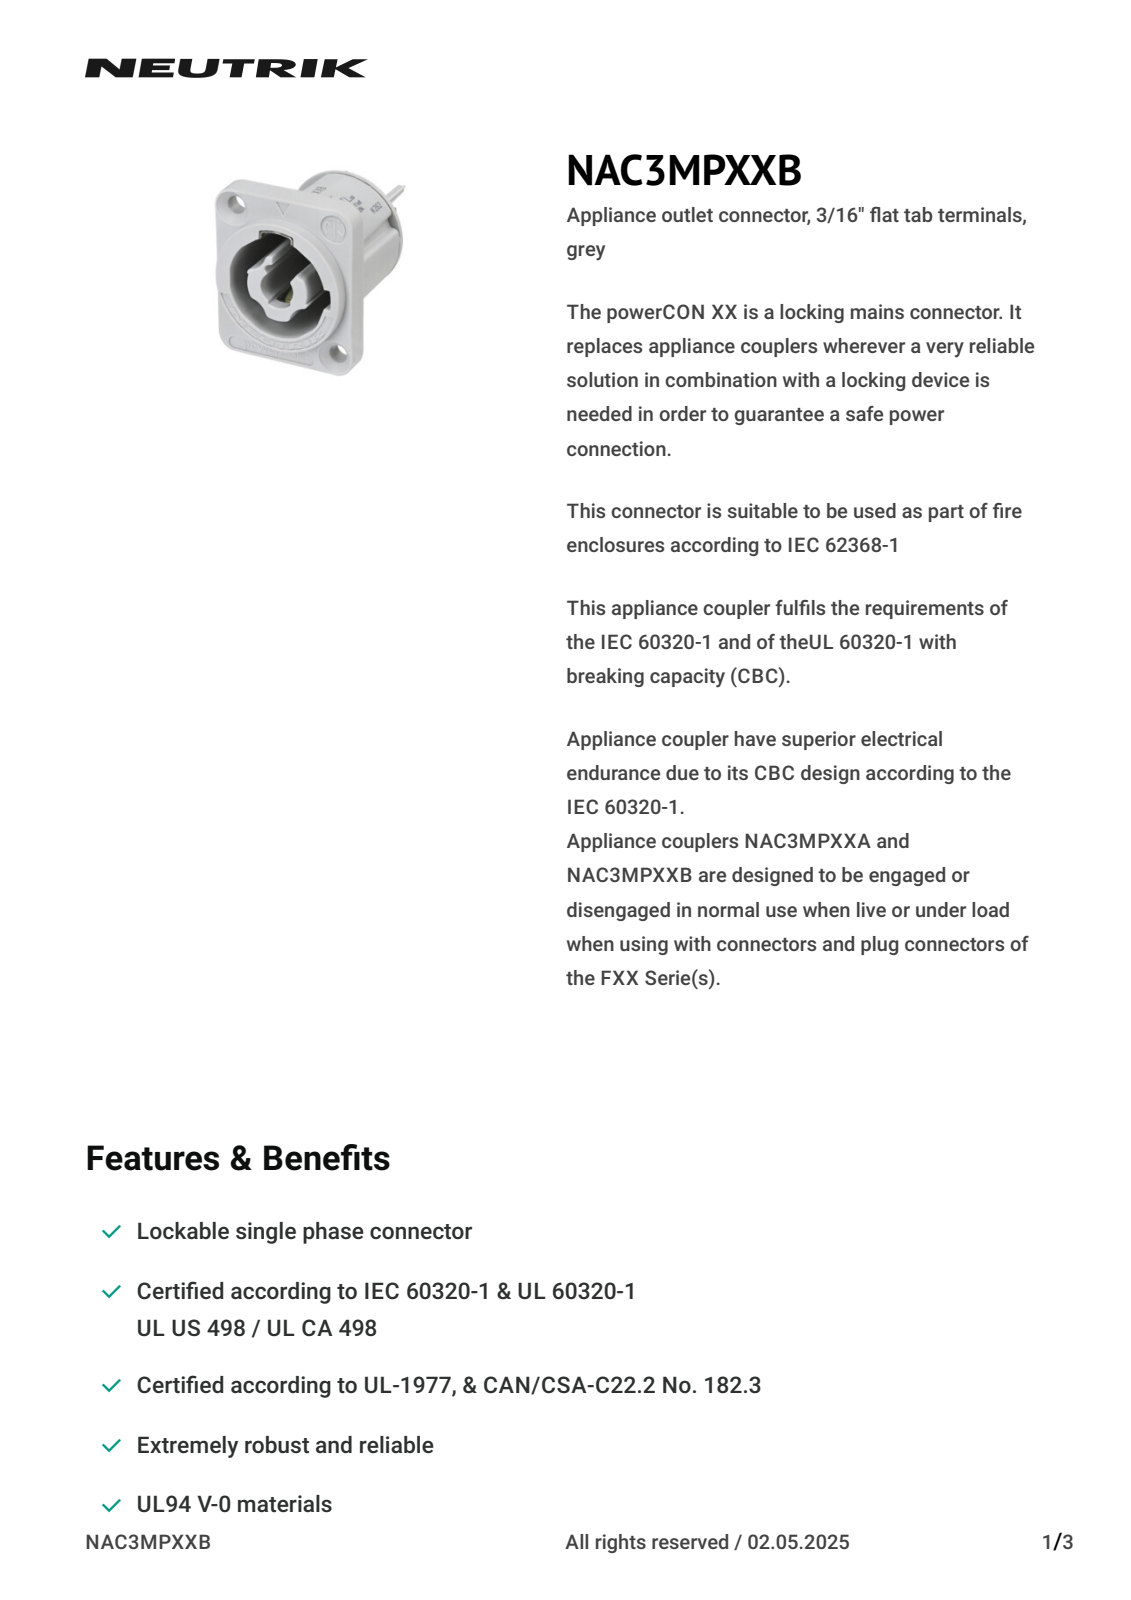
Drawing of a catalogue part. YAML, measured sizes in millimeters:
part_name: "30009536"
step_written_by: "CREO PARAMETRIC BY PTC INC, 2021184 (CONFIG_CONTROL_DESIGN)"
units: millimeters
bodies: {solids: 1, faces: 1004, planar: 254, cylindrical: 143, other: 607}
overall_size: [34.3, 30.9, 25.9]
volume: 9605
surface_area: 5317
round_holes:
  - {diameter: 1.4, count: 2}
  - {diameter: 6, count: 2}
  - {diameter: 5, count: 1}
round_bosses_or_shafts:
  - {diameter: 19, count: 1}
partial_cylinders:
  - {radius: 0.2, count: 28}
  - {radius: 0.3, count: 26}
  - {radius: 0.5, count: 19}
  - {radius: 0.25, count: 11}
  - {radius: 0.21, count: 9}
  - {radius: 1, count: 3}
  - {radius: 0.6, count: 2}
  - {radius: 0.75, count: 2}
face_to_face_distances: [20.39, 22.61, 2.22, 4.5, 18.11, 2.28, 2.55, 25.16, 7.05, 4.77]
hole_center_spacings: [19, 24, 30.61]
